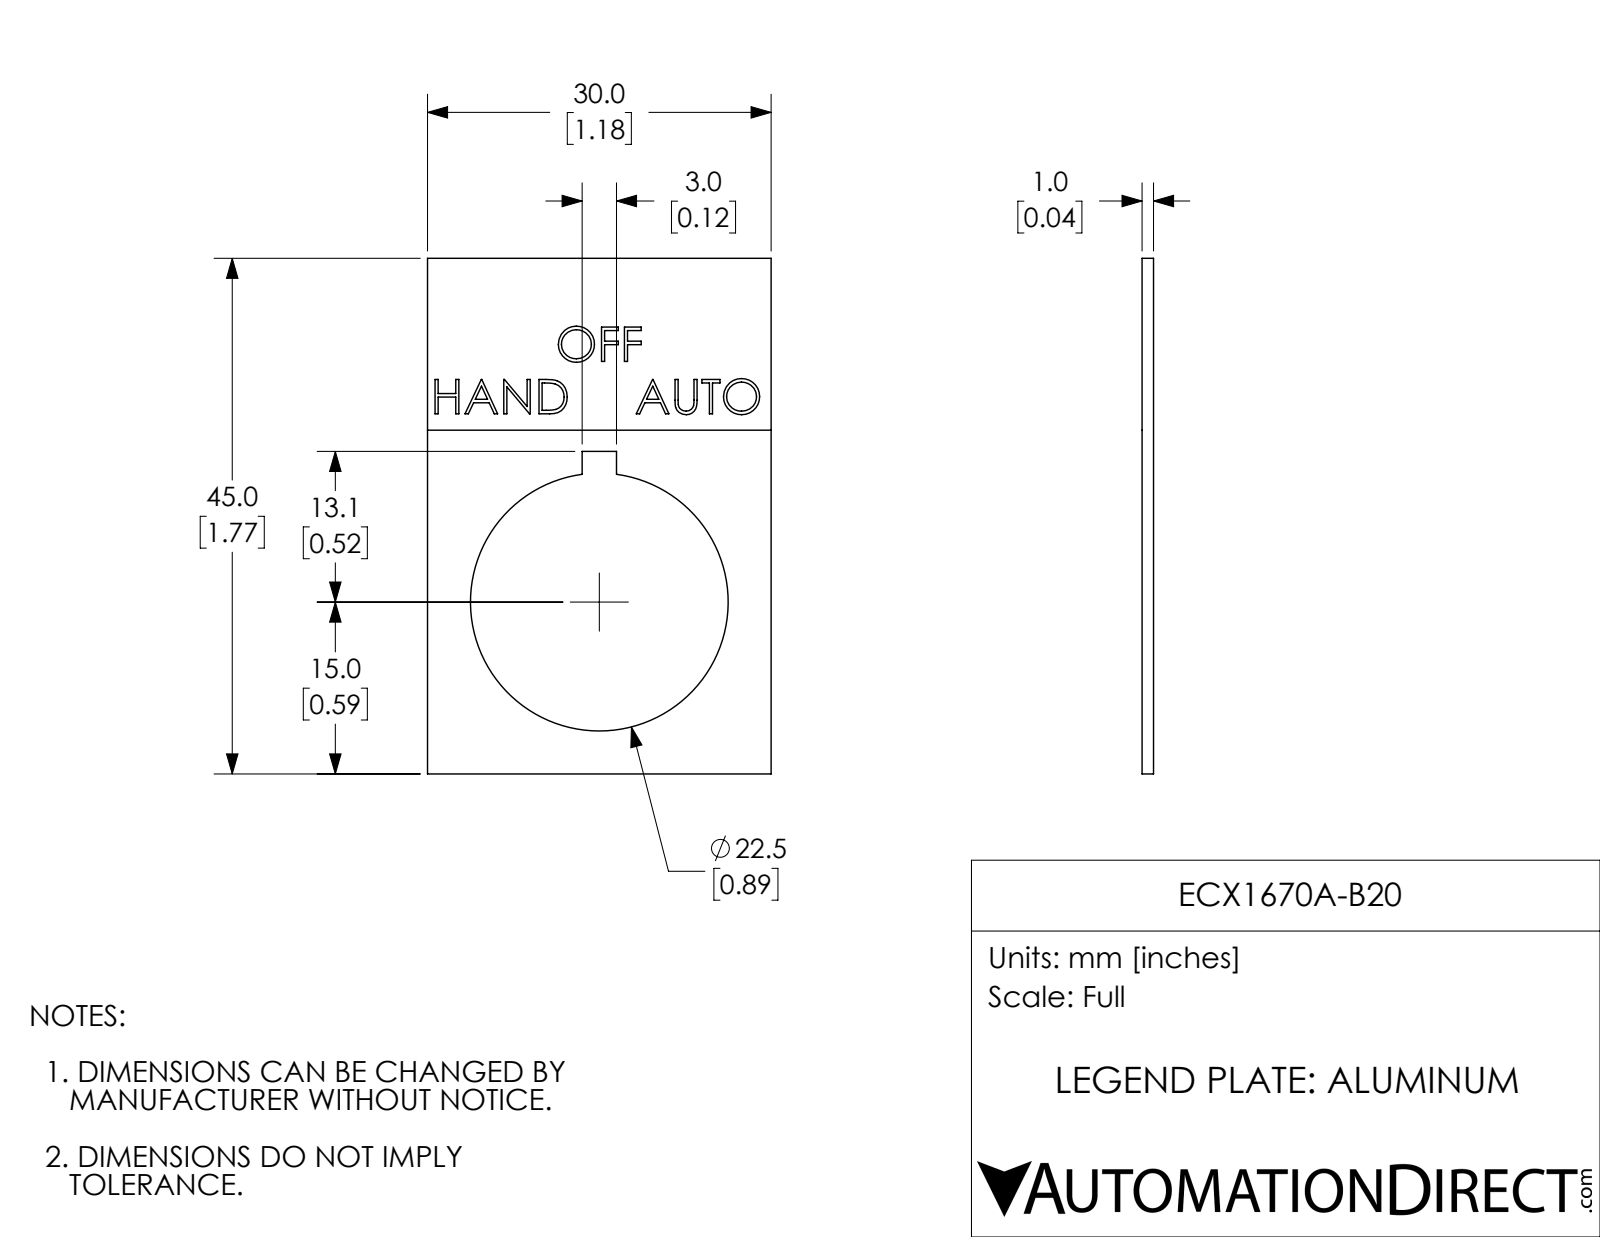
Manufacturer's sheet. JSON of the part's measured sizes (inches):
{"part_name": "ECX1670A-B20", "step_written_by": "SolidWorks 2017 (AUTOMOTIVE_DESIGN)", "units": "inches", "bodies": {"solids": 1, "faces": 143, "planar": 110, "cylindrical": 3, "other": 30}, "overall_size": [1.772, 1.181, 0.039], "volume_in3": 0.058, "surface_area_in2": 3.289, "round_holes": [[0.886, 1]], "face_to_face_distances": [0.039, 1.181, 1.772, 0.038, 0.531, 0.65, 1.108, 0.663, 0.118, 0.012]}
